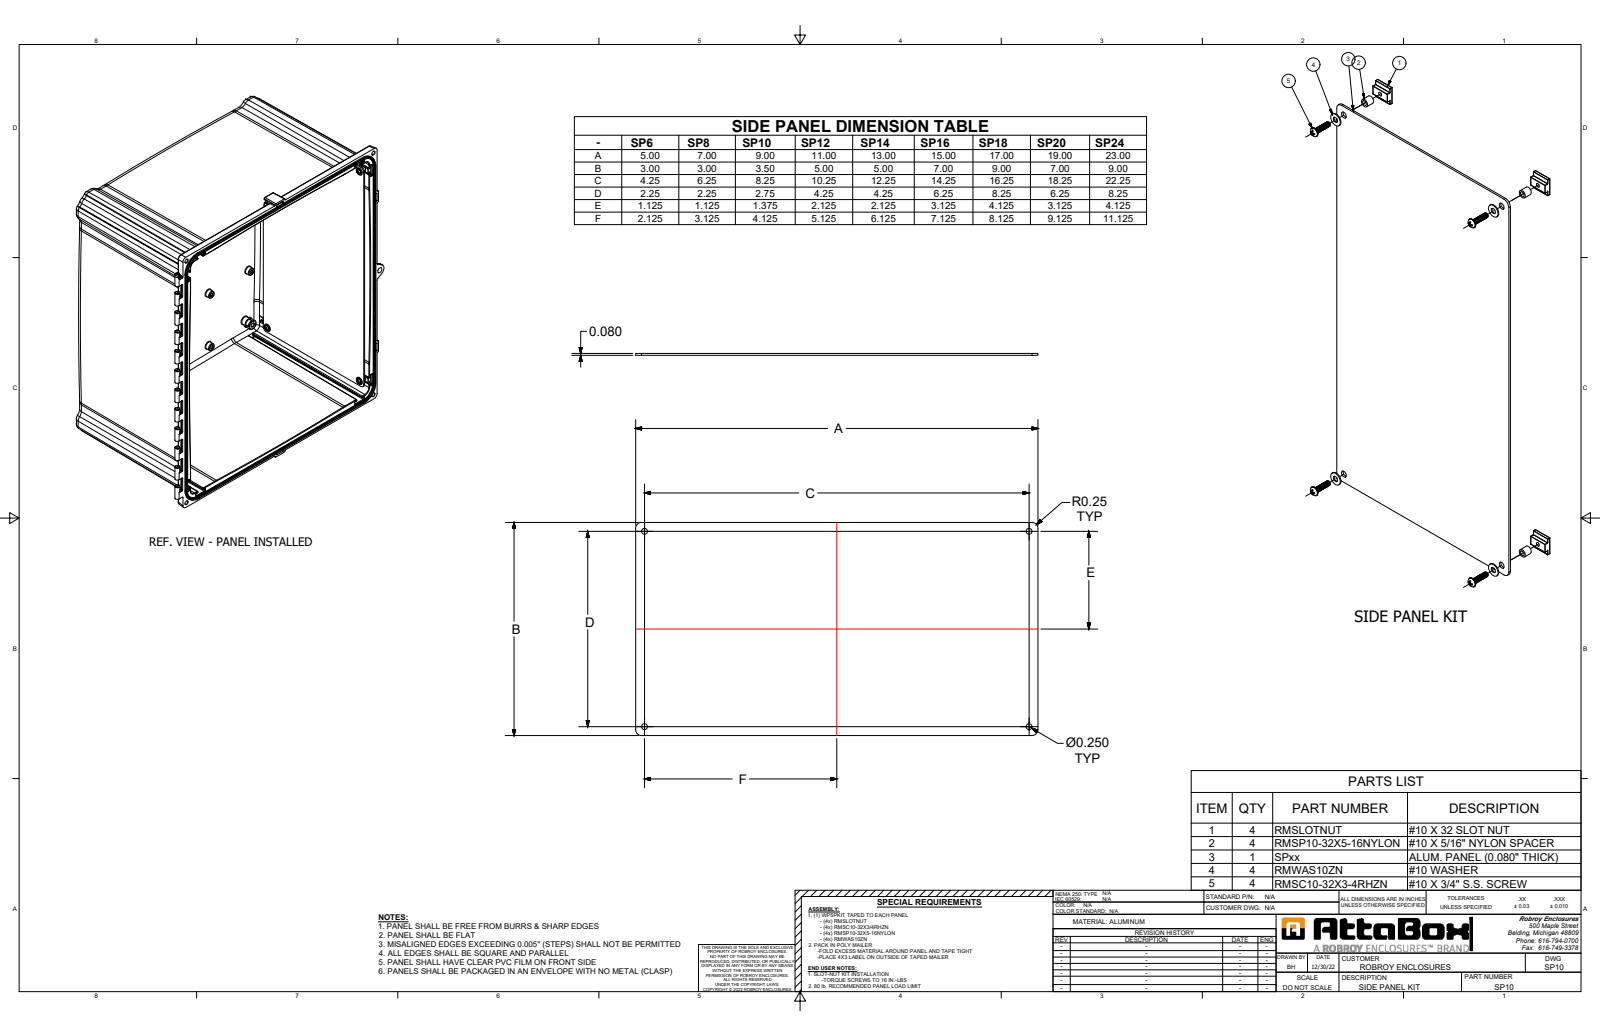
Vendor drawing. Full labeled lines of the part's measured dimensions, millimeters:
Part name (STEP PRODUCT): SP10_Default
STEP written by: SolidWorks 2023 (CONFIG_CONTROL_DESIGN)
Units: millimetres
Bodies: 1 solid, 14 faces (6 planar, 8 cylindrical, 0 other)
Overall size (bounding box): 228.6 × 88.9 × 2
Volume: 40 970 mm³ · Surface area: 41 750 mm²
Round holes (diameter × count): ⌀6.4 ×4
Partial cylindrical surfaces — rounded edges, fillets, slot ends (radius × count): R6.4 ×4
Main face-to-face distances: 2, 88.9, 228.6
Hole centre spacings: 69.9, 209.6, 220.9
